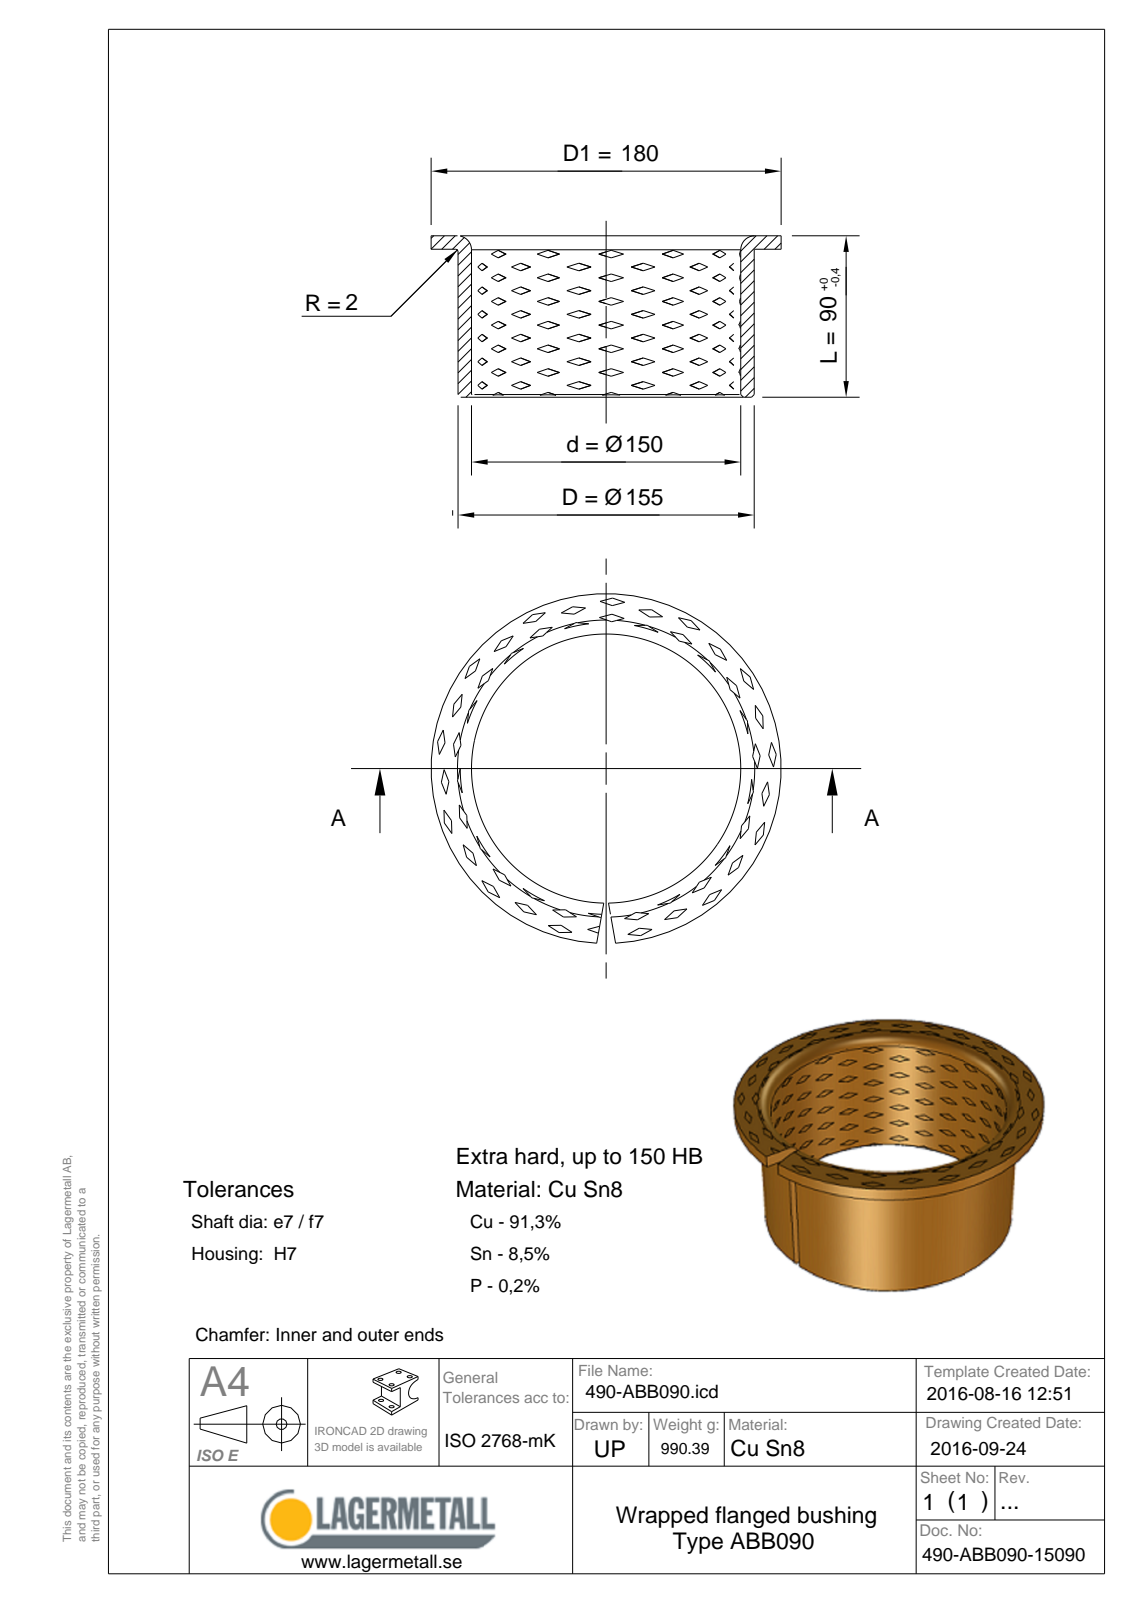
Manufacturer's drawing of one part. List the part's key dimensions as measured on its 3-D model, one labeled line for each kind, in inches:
STEP written by: Spatial InterOp 3D (CONFIG_CONTROL_DESIGN)
Units: inches
Bodies: 1 solid, 26 faces (5 planar, 9 cylindrical, 12 other)
Overall size (bounding box): 7.087 × 7.087 × 3.543
Volume: 7.461 in³ · Surface area: 156.1 in²
Round holes (diameter × count): ⌀5.906 ×1
Round bosses / shafts (diameter × count): ⌀7.087 ×1, ⌀6.102 ×1
Main face-to-face distances: 0.098, 3.445, 3.543
